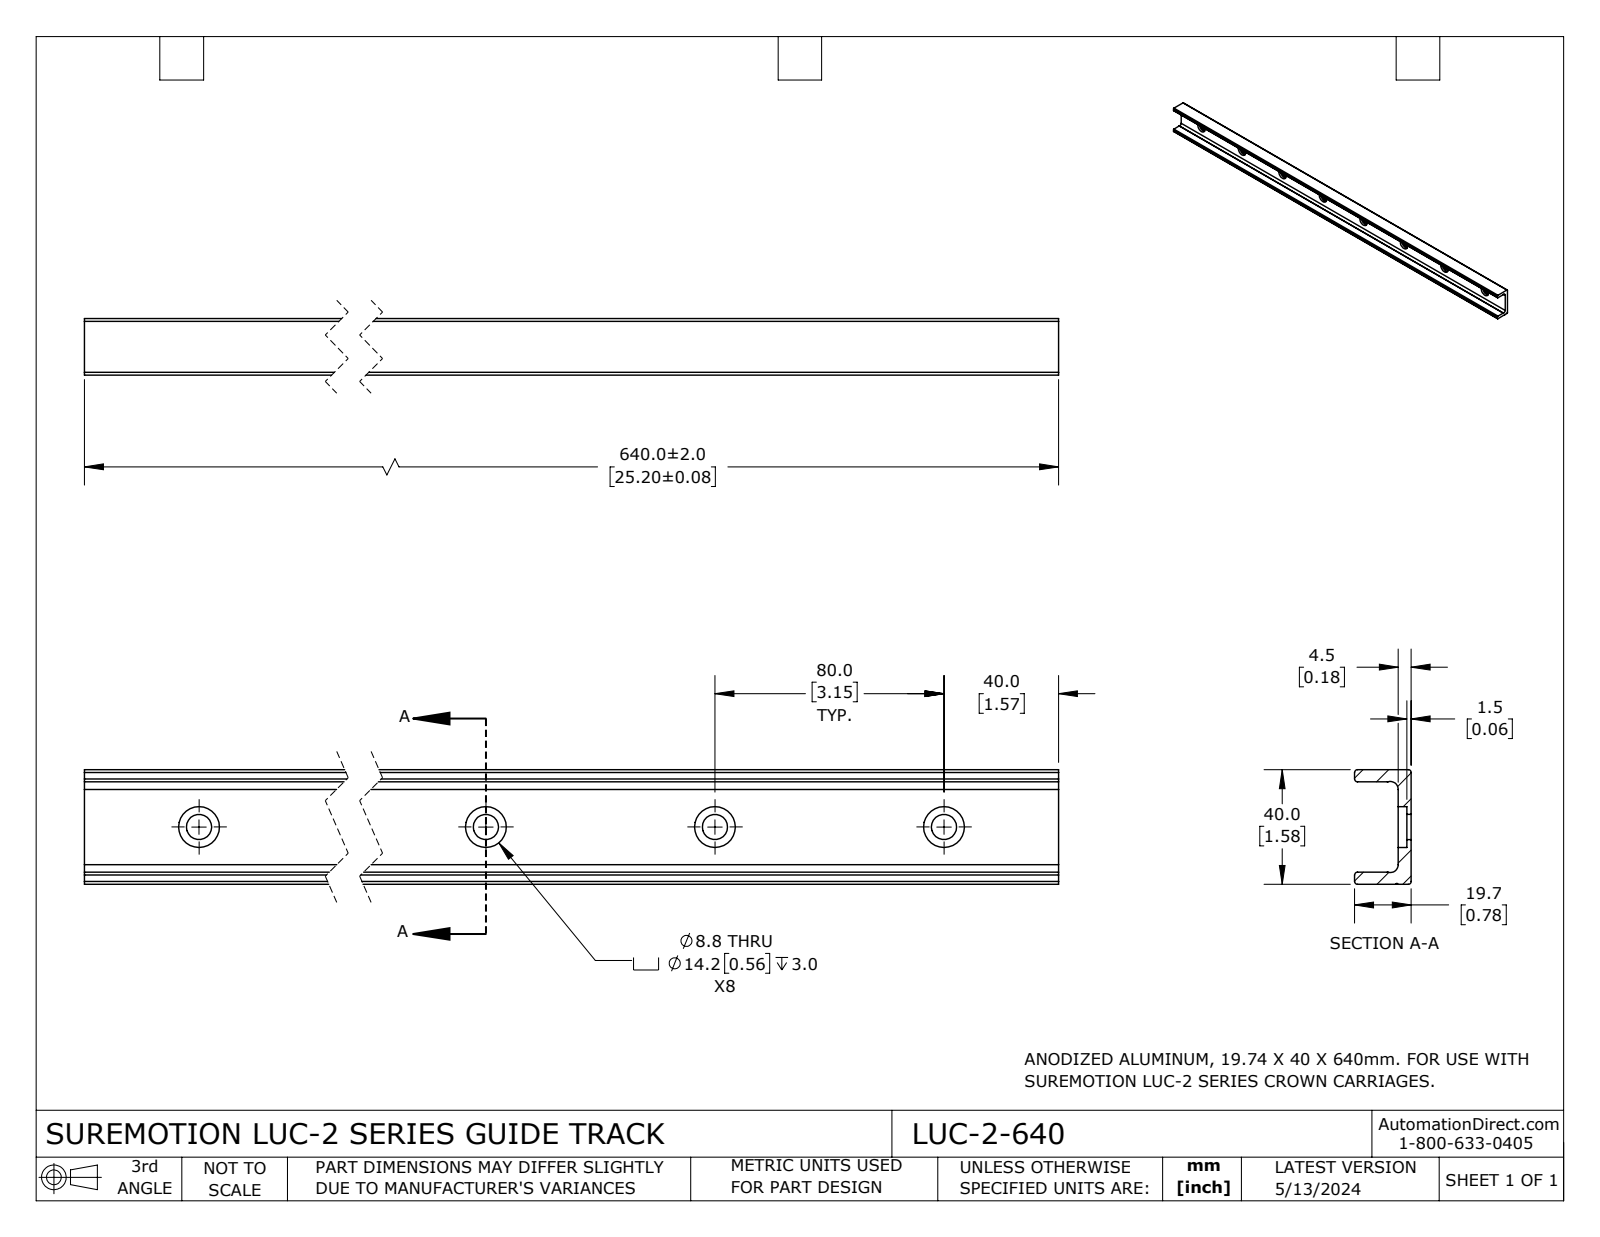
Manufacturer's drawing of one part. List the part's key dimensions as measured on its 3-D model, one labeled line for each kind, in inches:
Part name (STEP PRODUCT): LUC-2-640
STEP written by: SolidWorks 2023 (CONFIG_CONTROL_DESIGN)
Units: inches
Bodies: 1 solid, 62 faces (19 planar, 43 cylindrical, 0 other)
Overall size (bounding box): 25.197 × 1.575 × 0.777
Volume: 11.85 in³ · Surface area: 146.2 in²
Round holes (diameter × count): ⌀0.347 ×8, ⌀0.561 ×8
Partial cylindrical surfaces — rounded edges, fillets, slot ends (radius × count): R0.039 ×8, R0.109 ×2, R0.013 ×1
Main face-to-face distances: 0.177, 0.168, 1.408, 1.576, 1.24, 0.777, 0.6, 0.059, 0.118, 0.718
Hole centre spacings: 3.15, 6.299, 9.449, 12.598, 15.748, 18.898, 22.047
